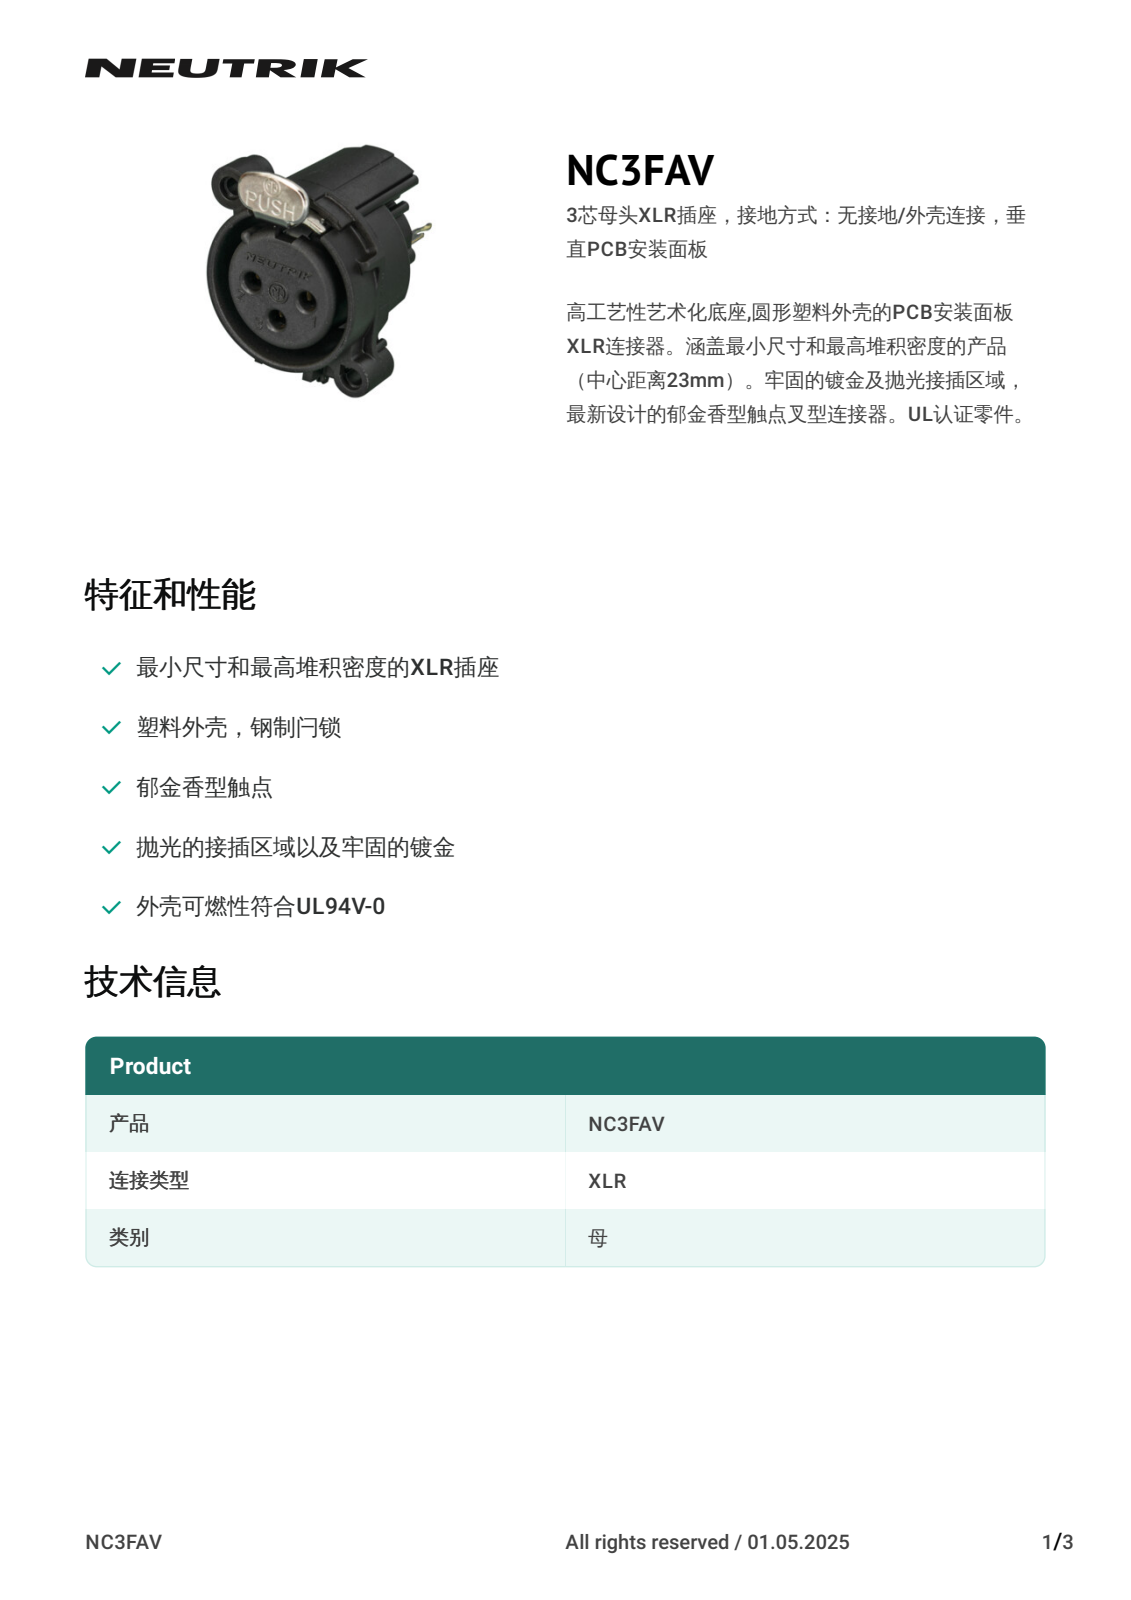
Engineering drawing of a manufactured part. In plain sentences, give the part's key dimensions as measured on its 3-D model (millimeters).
The part is named "NC3FAV". Its 3-D file was written by "CREO PARAMETRIC BY PTC INC, 2023424 (AUTOMOTIVE_DESIGN)". It is 1 solid with 2008 faces: 1149 planar, 416 cylindrical and 443 other. Overall it measures 35.47 by 30.64 by 25.3 millimeters. Its volume is 4 997 cubic millimeters and its surface area 6 494 square millimeters. Round holes: 4 of diameter 2.5, 2 of diameter 2.35, 2 of diameter 3, 1 of diameter 2.51, 1 of diameter 19.5, 1 of diameter 21.8. Round bosses or shafts: 3 of diameter 1.5, 1 of diameter 15.8, 1 of diameter 5.8, 1 of diameter 3, 1 of diameter 2.19. Partial cylindrical surfaces (rounded edges, fillets, slot ends): 144 of radius 0.2, 29 of radius 0.15, 27 of radius 1, 20 of radius 0.5, 12 of radius 0.4, 9 of radius 0.12, 9 of radius 0.3, 9 of radius 0.6. The main face-to-face distances are 0.5, 1.5, 1, 13, 5.72, 10.3, 0.7, 6.55, 14.5, 20.22. The hole center spacings are 4.05, 5.66, 11.5, 14, 15.62, 17.11, 3.95, 8.1.
